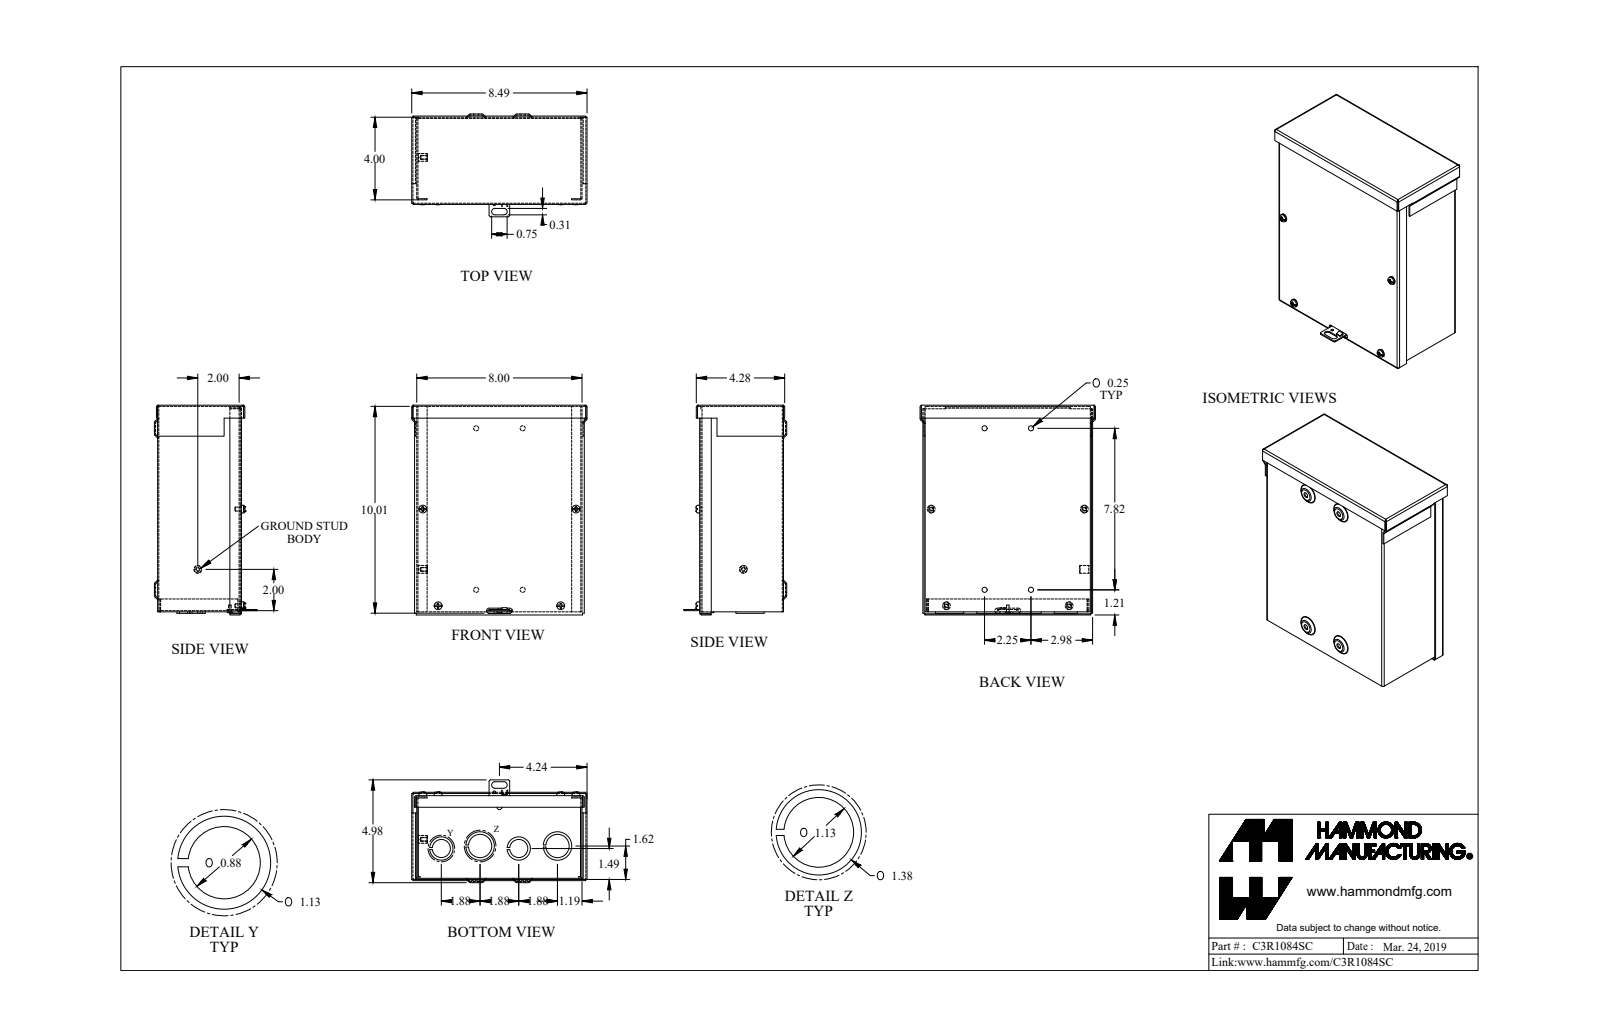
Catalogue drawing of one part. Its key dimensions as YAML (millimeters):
part_name: "C3R1084SC_Default"
step_written_by: "SolidWorks 2019 (CONFIG_CONTROL_DESIGN)"
units: millimeters
bodies: {solids: 11, faces: 424, planar: 223, cylindrical: 115, other: 86}
overall_size: [257.8, 215.6, 126.4]
volume: 343300
surface_area: 478500
round_holes:
  - {diameter: 4.3, count: 4}
  - {diameter: 6.4, count: 4}
  - {diameter: 28.6, count: 2}
  - {diameter: 3.2, count: 1}
  - {diameter: 3.5, count: 1}
  - {diameter: 4, count: 1}
  - {diameter: 22.2, count: 1}
  - {diameter: 22.2, count: 1}
round_bosses_or_shafts:
  - {diameter: 9.5, count: 4}
  - {diameter: 4.8, count: 4}
  - {diameter: 34.9, count: 2}
  - {diameter: 28.6, count: 2}
  - {diameter: 9.5, count: 1}
  - {diameter: 3.2, count: 1}
partial_cylinders:
  - {radius: 0.7, count: 21}
  - {radius: 2.2, count: 21}
  - {radius: 2.8, count: 8}
  - {radius: 3.2, count: 8}
  - {radius: 4, count: 2}
face_to_face_distances: [1.4, 101.6, 100.2, 103, 201.8, 203.2, 1.4, 200.3, 251.1, 252.6]
hole_center_spacings: [119, 157.9, 47.8, 50.7, 57.2, 95.3, 105.8, 120.3]
